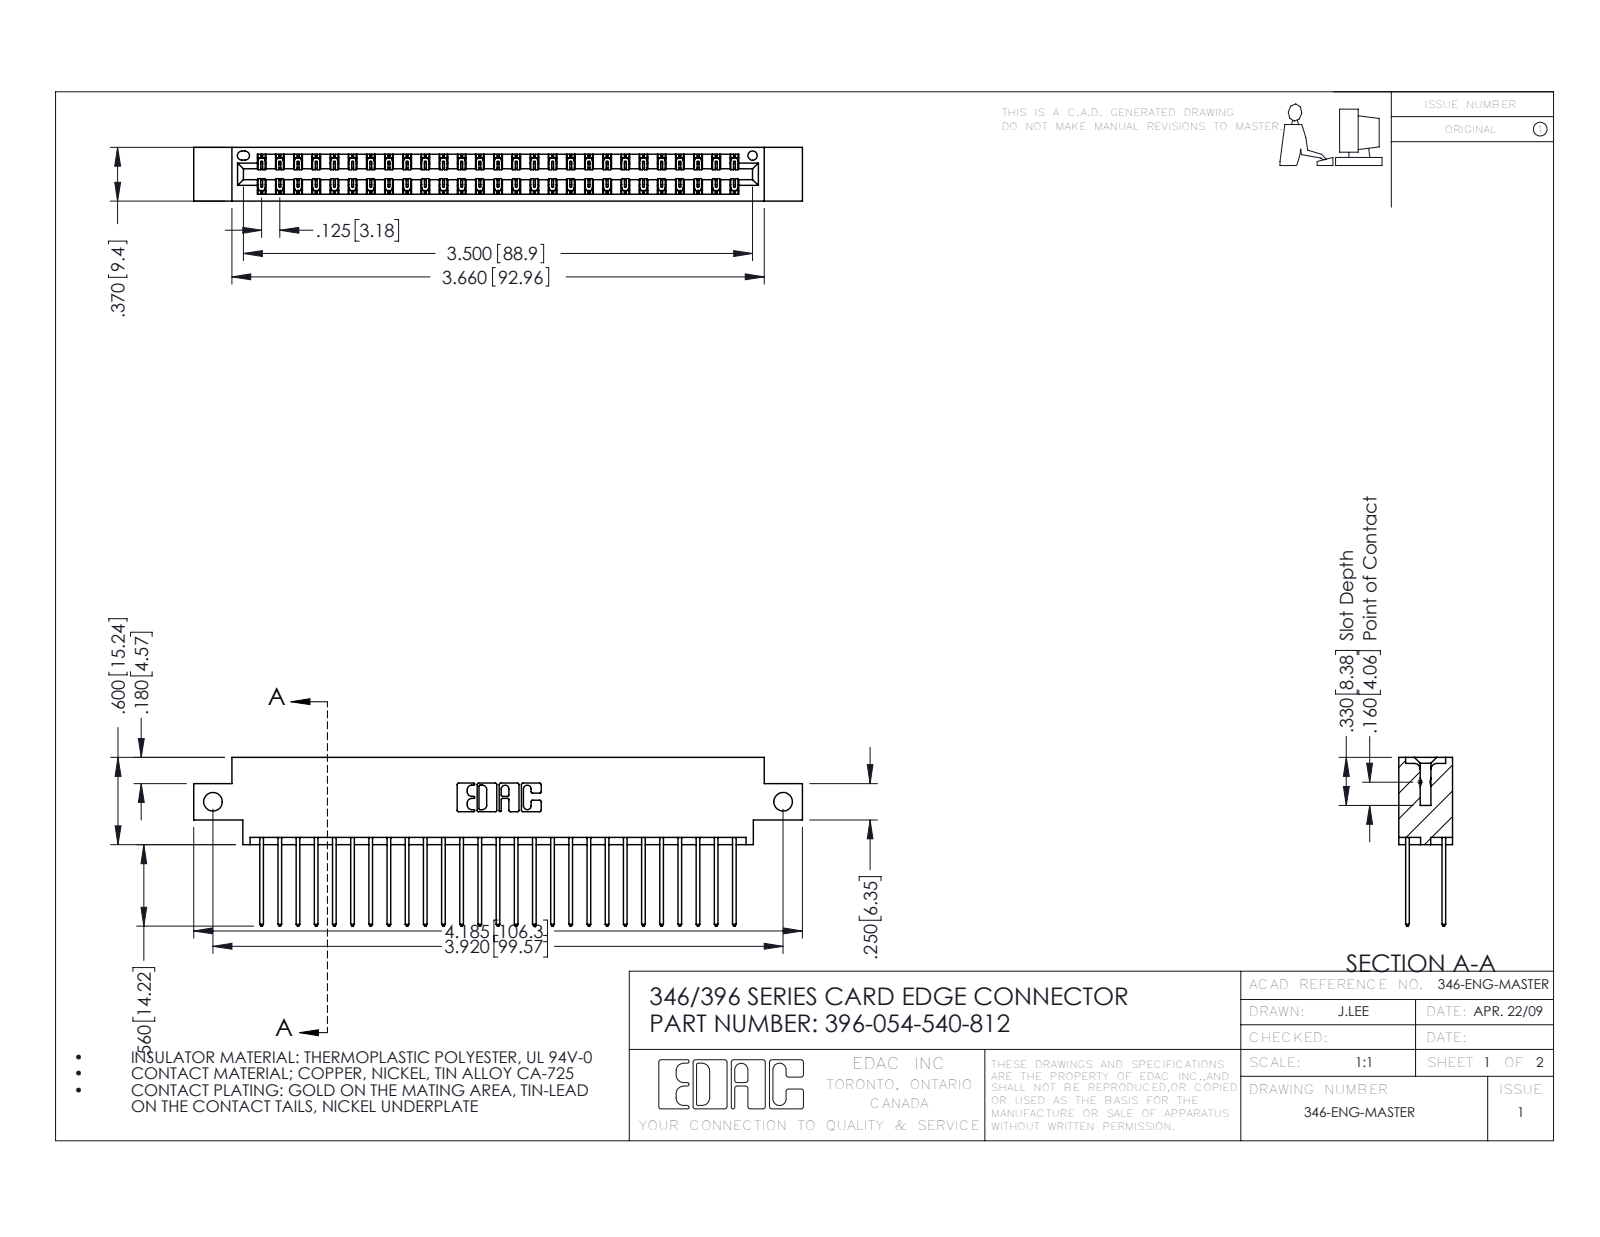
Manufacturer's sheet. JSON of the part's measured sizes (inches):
{"part_name": "345-292-001_345-293-140; 396-054-540-812; 346 Part_0.170 Offset - Side Mount", "step_written_by": "SolidWorks 2016 (CONFIG_CONTROL_DESIGN)", "units": "inches", "bodies": {"solids": 55, "faces": 2934, "planar": 1970, "cylindrical": 964, "other": 0}, "overall_size": [4.185, 1.16, 0.37], "volume_in3": 0.623, "surface_area_in2": 22.96, "round_holes": [[0.128, 2], [0.064, 1]], "partial_cylinders_radius": [[0.006, 81], [0.01, 54], [0.01, 22], [0.007, 6], [0.031, 6], [0.026, 3], [0.014, 2], [0.022, 2]], "face_to_face_distances": [0.048, 0.322, 0.25, 0.37, 0.072, 0.298, 0.025, 0.275, 0.148, 0.222], "hole_center_spacings": [3.92]}
